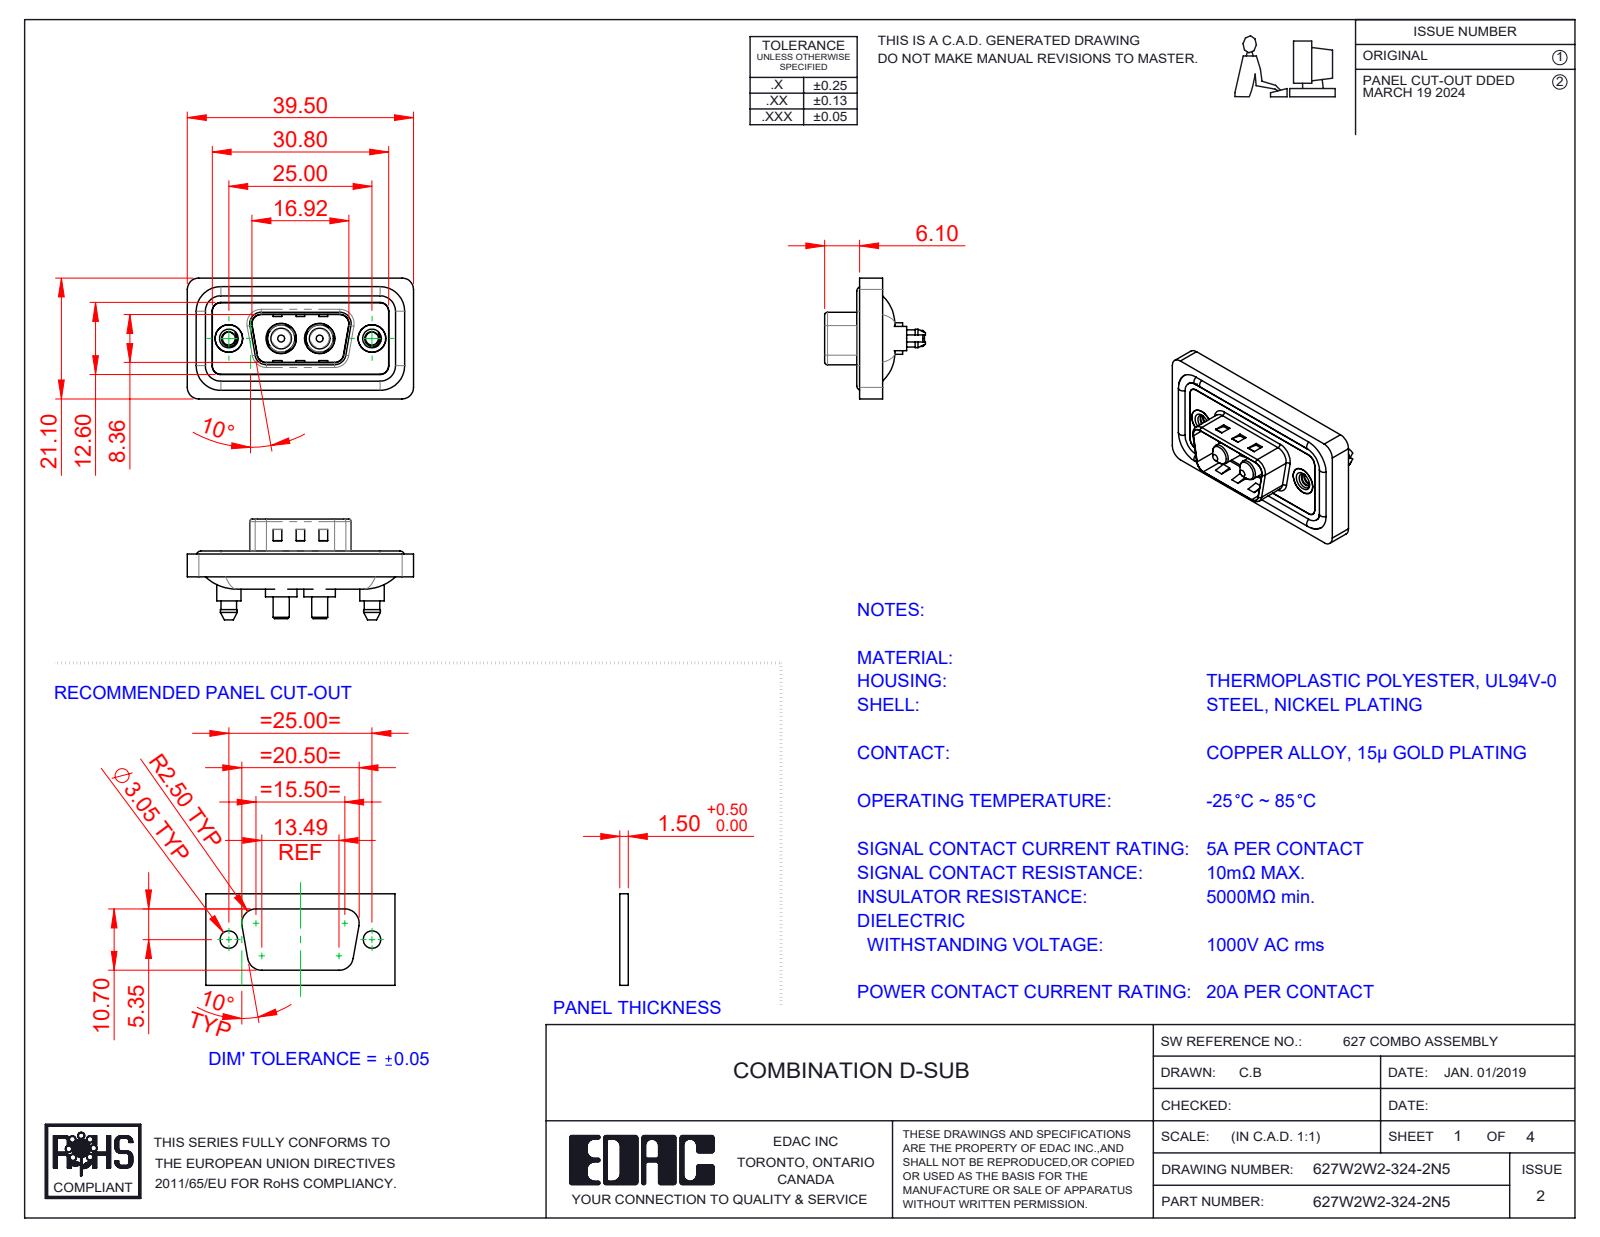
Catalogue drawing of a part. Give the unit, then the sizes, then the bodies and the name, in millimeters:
Units: millimetres
Overall size (bounding box): 39.5 × 21.1 × 17.6
Round holes (diameter × count): ⌀2.26 ×2, ⌀4 ×2, ⌀4.8 ×2, ⌀4.85 ×2, ⌀5 ×2, ⌀5.3 ×2
Round bosses / shafts (diameter × count): ⌀1.6 ×4, ⌀5.5 ×2, ⌀5.4 ×2, ⌀5.2 ×2, ⌀4.9 ×2, ⌀4.75 ×2, ⌀4.25 ×2, ⌀3.75 ×2
Partial cylindrical surfaces — rounded edges, fillets, slot ends (radius × count): R1.5 ×24, R2 ×18, R1.6 ×10, R0.5 ×8, R0.25 ×4, R0.6 ×4, R0.65 ×4, R0.9 ×4
Main face-to-face distances: 0.4, 1.1, 2.9, 3.1, 0.5, 1.6, 1.5, 4, 0.7, 2.5
Hole centre spacings: 9.14, 15.86, 6.72, 25
Volume: 4 594 mm³ · Surface area: 7 317 mm²
Bodies: 11 solids, 539 faces (181 planar, 250 cylindrical, 108 other)
Part name (STEP PRODUCT): 627Combo Waterproof Housing_09 Contacts; 627W2W2-324-2N5; 627Combo Threaded Boardlock_5; 627Combo Shell Rear_09 Contacts (+3 more)
STEP written by: SolidWorks 2023 (CONFIG_CONTROL_DESIGN)
